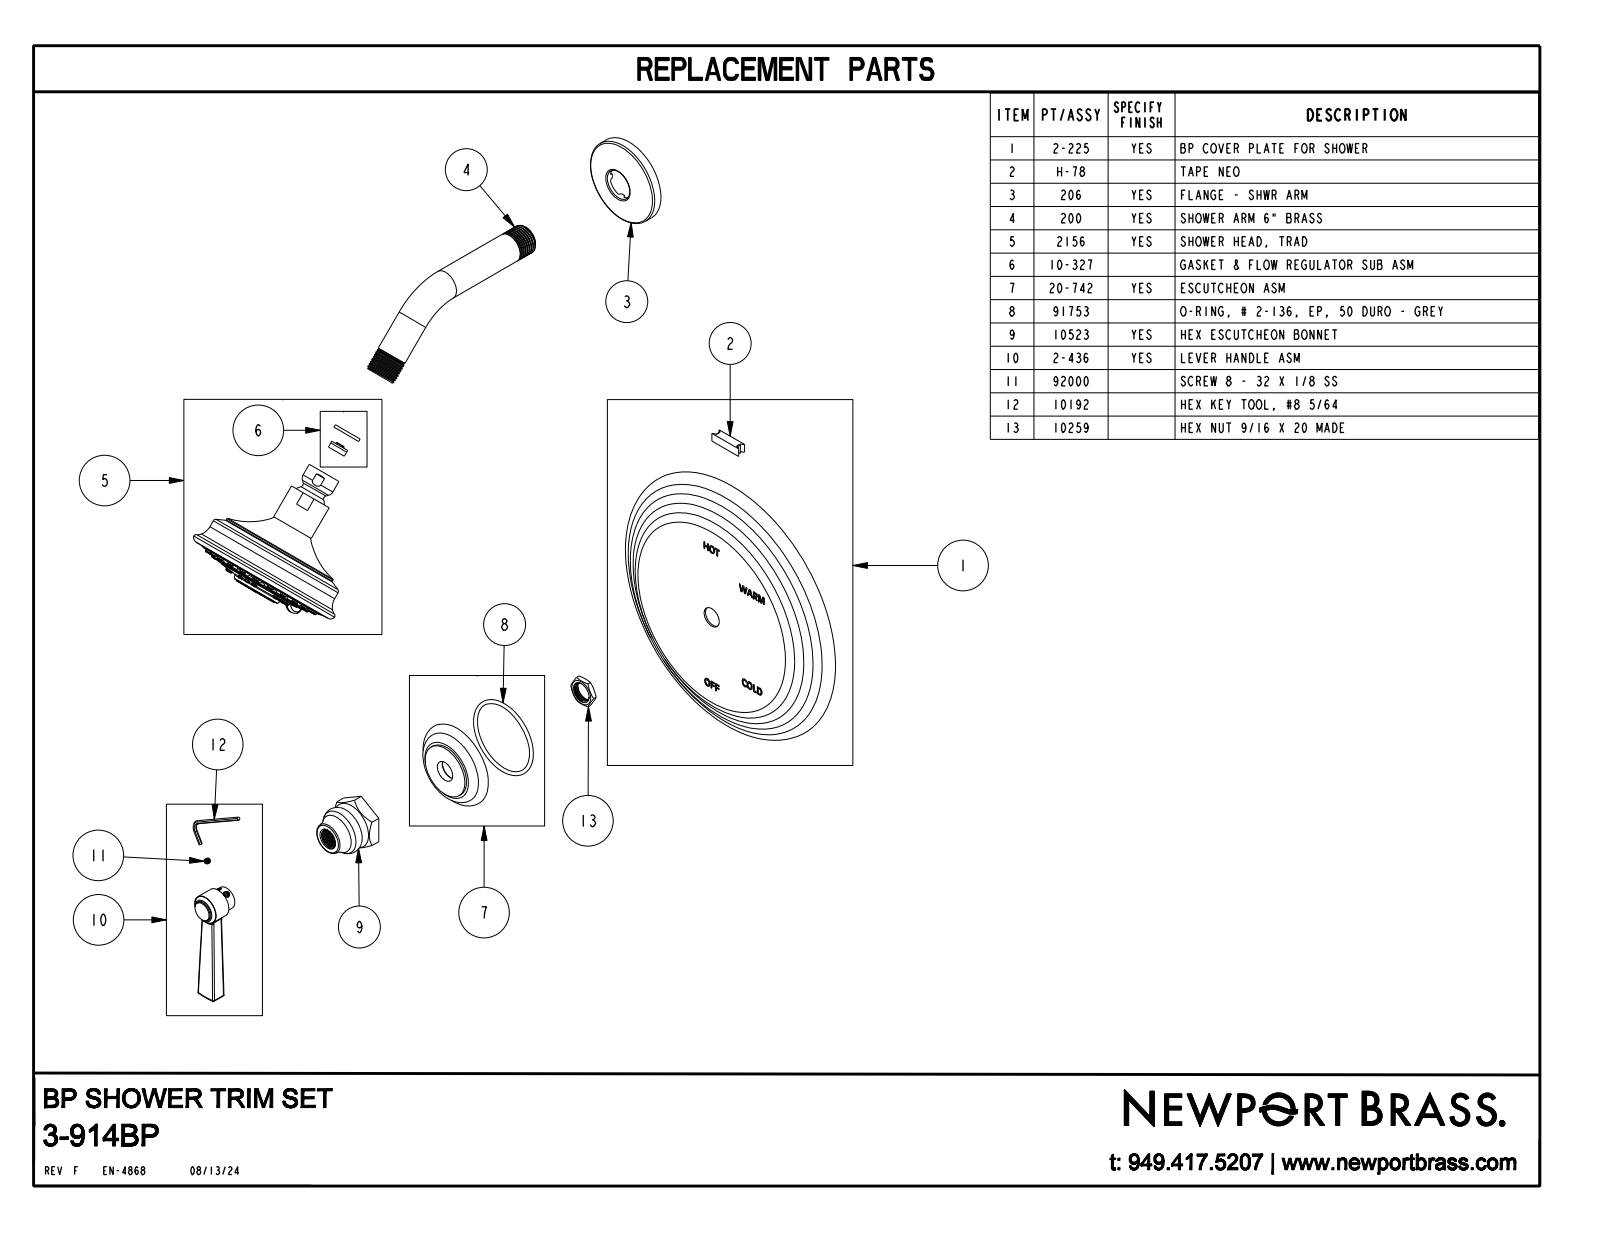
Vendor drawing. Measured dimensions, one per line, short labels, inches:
name: 3-914BP
written by: CREO PARAMETRIC BY PTC INC, 2018400 (CONFIG_CONTROL_DESIGN)
unit: in
bodies: 2 solids, 1354 faces (281 planar, 206 cylindrical, 867 other)
size: 17.065 × 8.25 × 7.75
volume: 51.28 in³; area: 189.8 in²
holes: 8× ⌀0.059, 1× ⌀0.925
bosses: 39× ⌀0.142, 23× ⌀0.165, 2× ⌀0.813, 1× ⌀3.81, 1× ⌀3.724, 1× ⌀3.24, 1× ⌀2.38, 1× ⌀2.323
rounds: 8× R0.079, 2× R0.02, 2× R0.04, 2× R0.055, 1× R0.138, 1× R0.472, 1× R0.512, 1× R0.63
face distances: 0.754, 0.063, 0.118, 0.181, 1.313, 0.062, 2.441, 1.687, 1.129, 0.375
hole spacings: 0.443, 0.579, 0.818, 0.819, 1.069, 0.443, 0.578, 1.069
